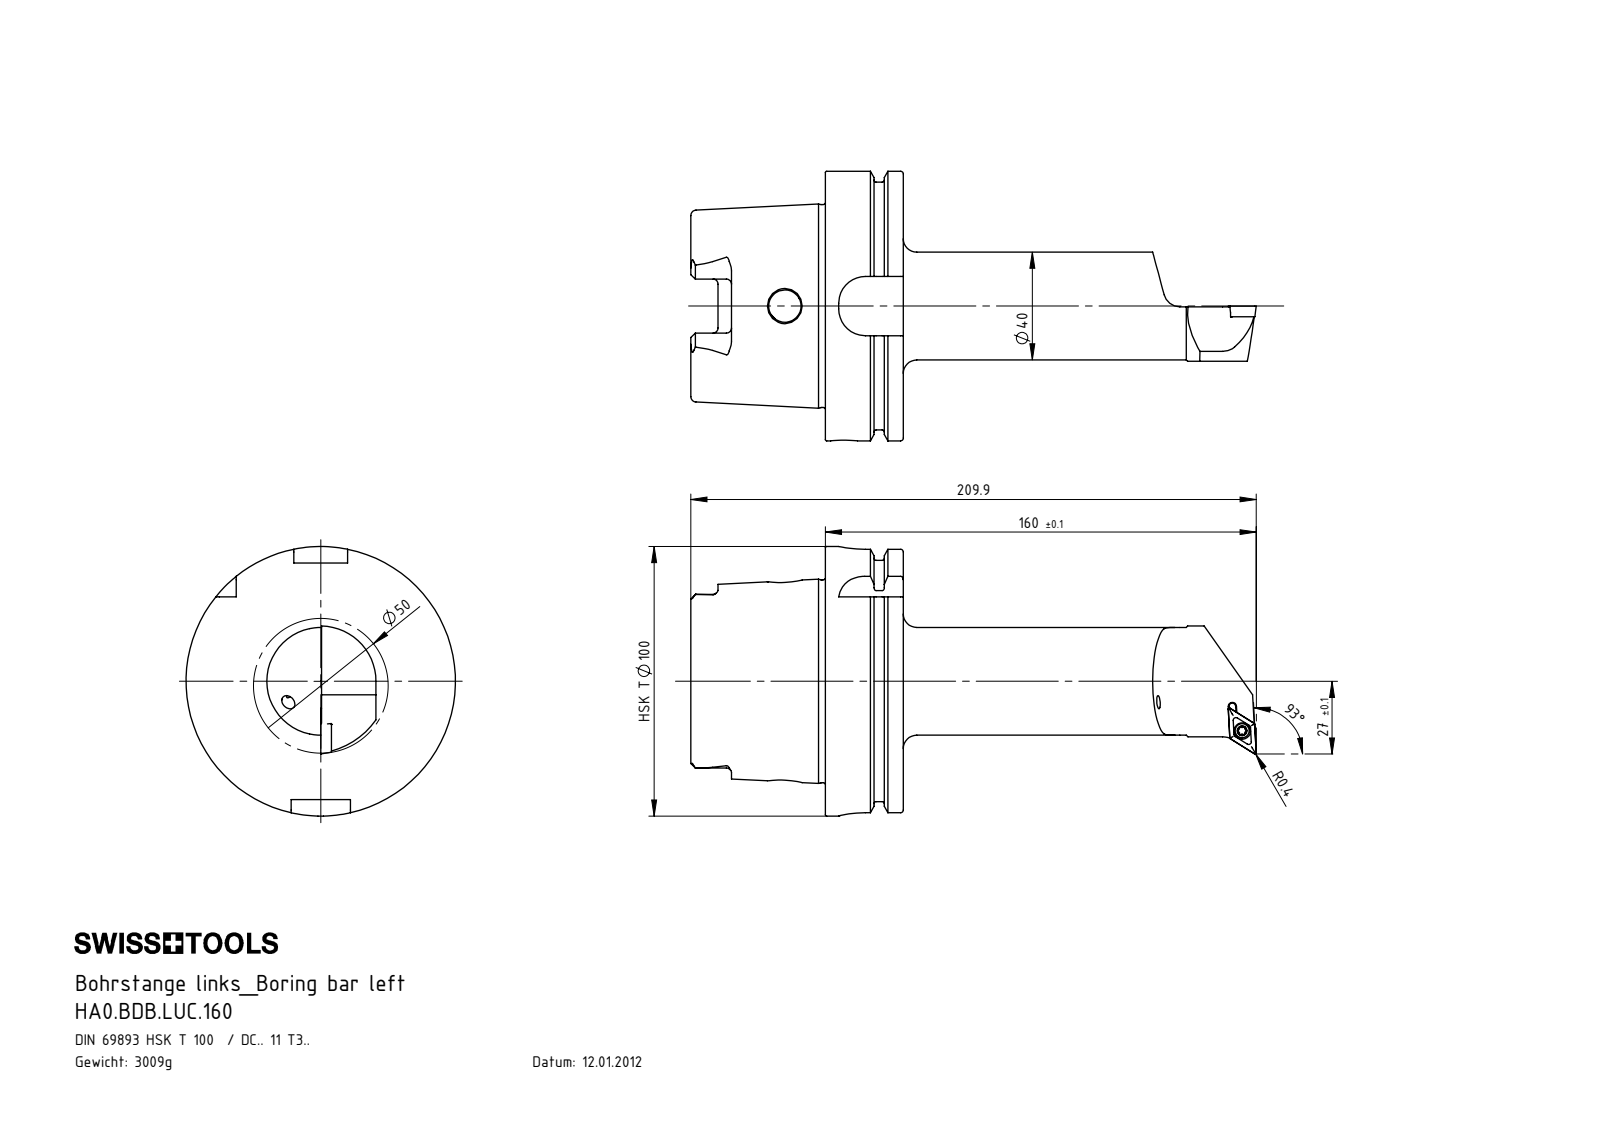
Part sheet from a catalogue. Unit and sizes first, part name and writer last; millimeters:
Units: millimetres
Overall size (bounding box): 209.9 × 100 × 100
Round holes (diameter × count): ⌀4.2 ×2, ⌀12 ×2, ⌀3.3 ×1, ⌀4 ×1, ⌀4.4 ×1, ⌀6.1 ×1, ⌀10 ×1, ⌀22.5 ×1, ⌀26 ×1, ⌀53 ×1, ⌀63 ×1
Round bosses / shafts (diameter × count): ⌀100 ×1, ⌀91.95 ×1, ⌀75.26 ×1, ⌀40 ×1, ⌀5.25 ×1, ⌀5 ×1, ⌀4 ×1
Partial cylindrical surfaces — rounded edges, fillets, slot ends (radius × count): R0.34 ×6, R0.59 ×6, R1.9 ×6, R10 ×4, R4.83 ×2, R4.88 ×2, R1.25 ×1, R6 ×1
Main face-to-face distances: 28.95, 12.45, 16.5, 49.9, 62.35, 78.85, 87.8, 78.2, 28.3, 15.85
Hole centre spacings: 148.88, 148.95
Volume: 383 021 mm³ · Surface area: 69 244 mm²
Bodies: 5 solids, 311 faces (73 planar, 94 cylindrical, 144 other)
Part name (STEP PRODUCT): HA0-BDB.LUC.160_A_Fertigbearbeitung; WCB-ER2.001.009_A; HA0.BDB.LUC.160; DCMT11T304 (+1 more)
STEP written by: SolidWorks 2022 (AUTOMOTIVE_DESIGN)
